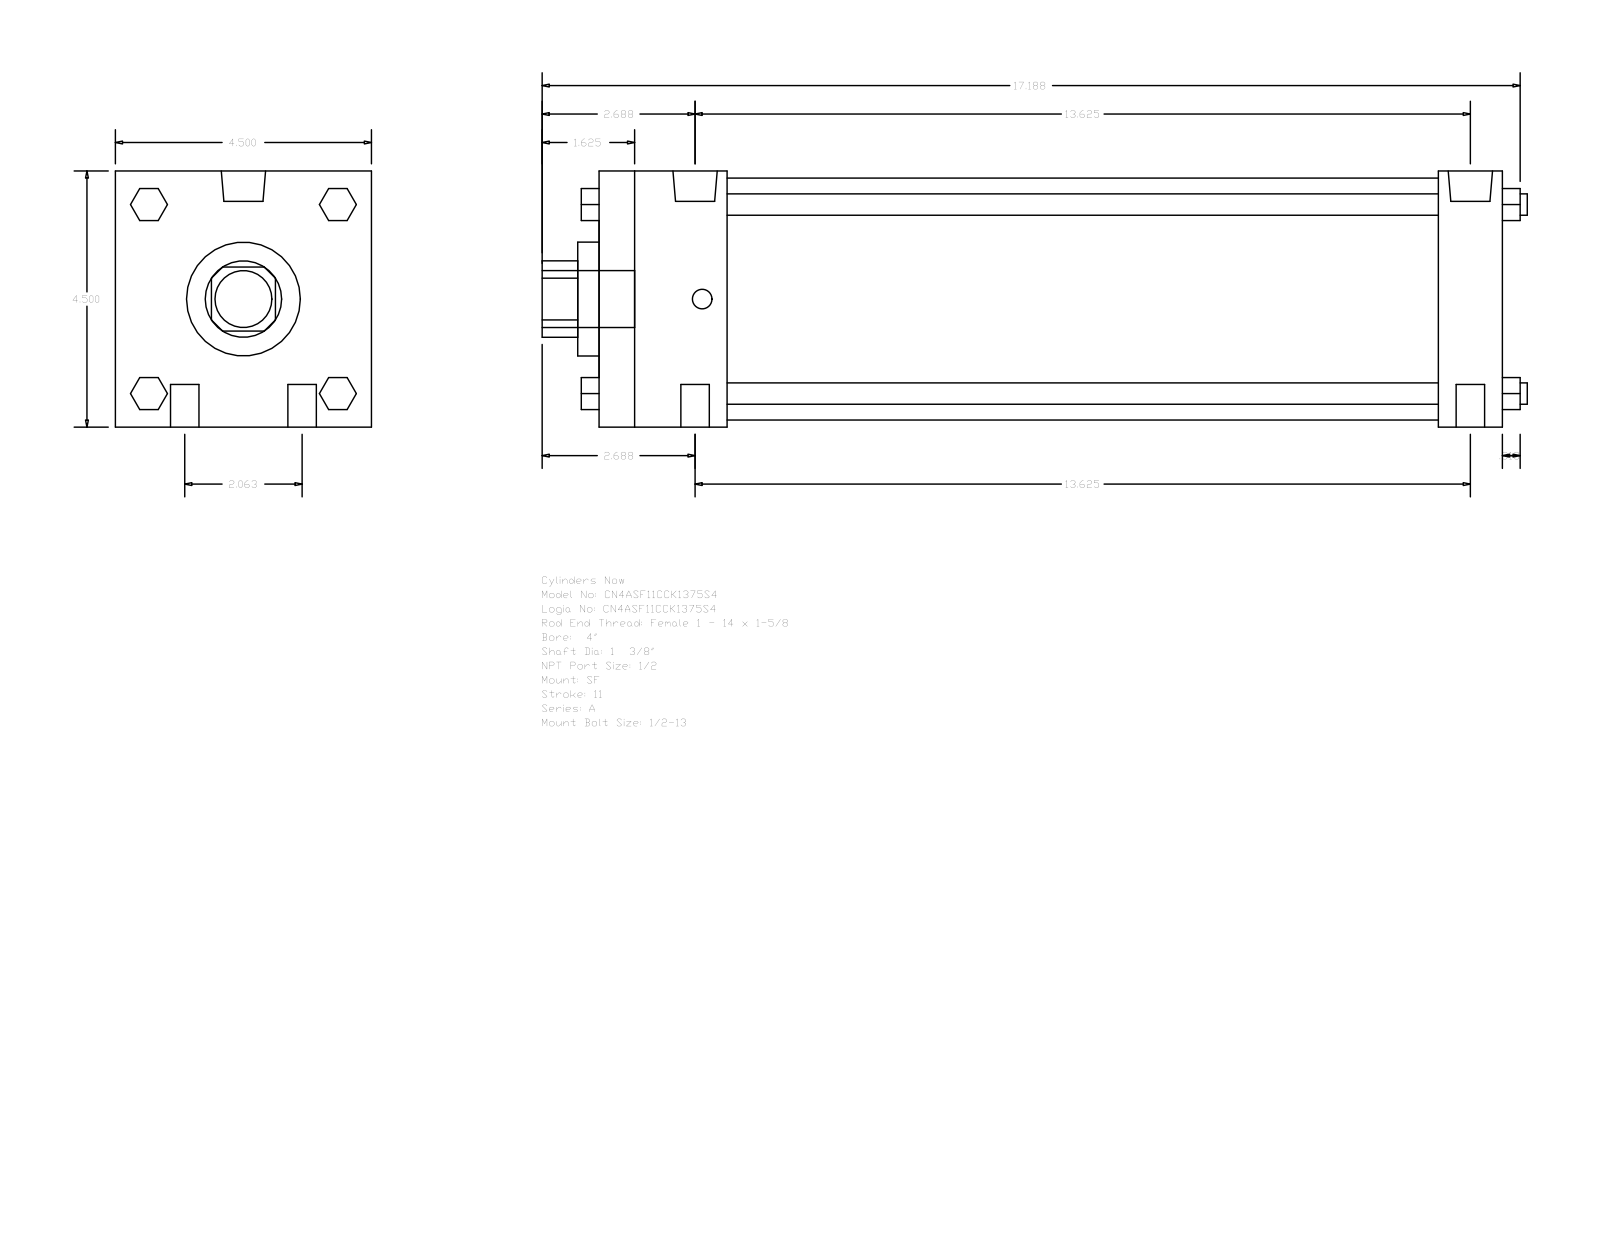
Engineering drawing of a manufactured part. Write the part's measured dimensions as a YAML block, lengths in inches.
part_name: "A_SF__0400_1.375"
step_written_by: "GSSL Pune (CONFIG_CONTROL_DESIGN)"
units: inches
bodies: {solids: 0, faces: 124, planar: 94, cylindrical: 30, other: 0}
overall_size: [17.313, 4.5, 4.5]
round_holes:
  - {diameter: 1.375, count: 1}
  - {diameter: 2, count: 1}
  - {diameter: 4.25, count: 1}
round_bosses_or_shafts:
  - {diameter: 0.5, count: 4}
  - {diameter: 0.375, count: 4}
  - {diameter: 0.778, count: 2}
  - {diameter: 0.344, count: 2}
  - {diameter: 1, count: 1}
partial_cylinders:
  - {radius: 0.672, count: 1}
face_to_face_distances: [4.5, 15.875, 1.125, 14.75, 2.25, 12.5, 13.625, 0.563, 0.375, 2.625]
